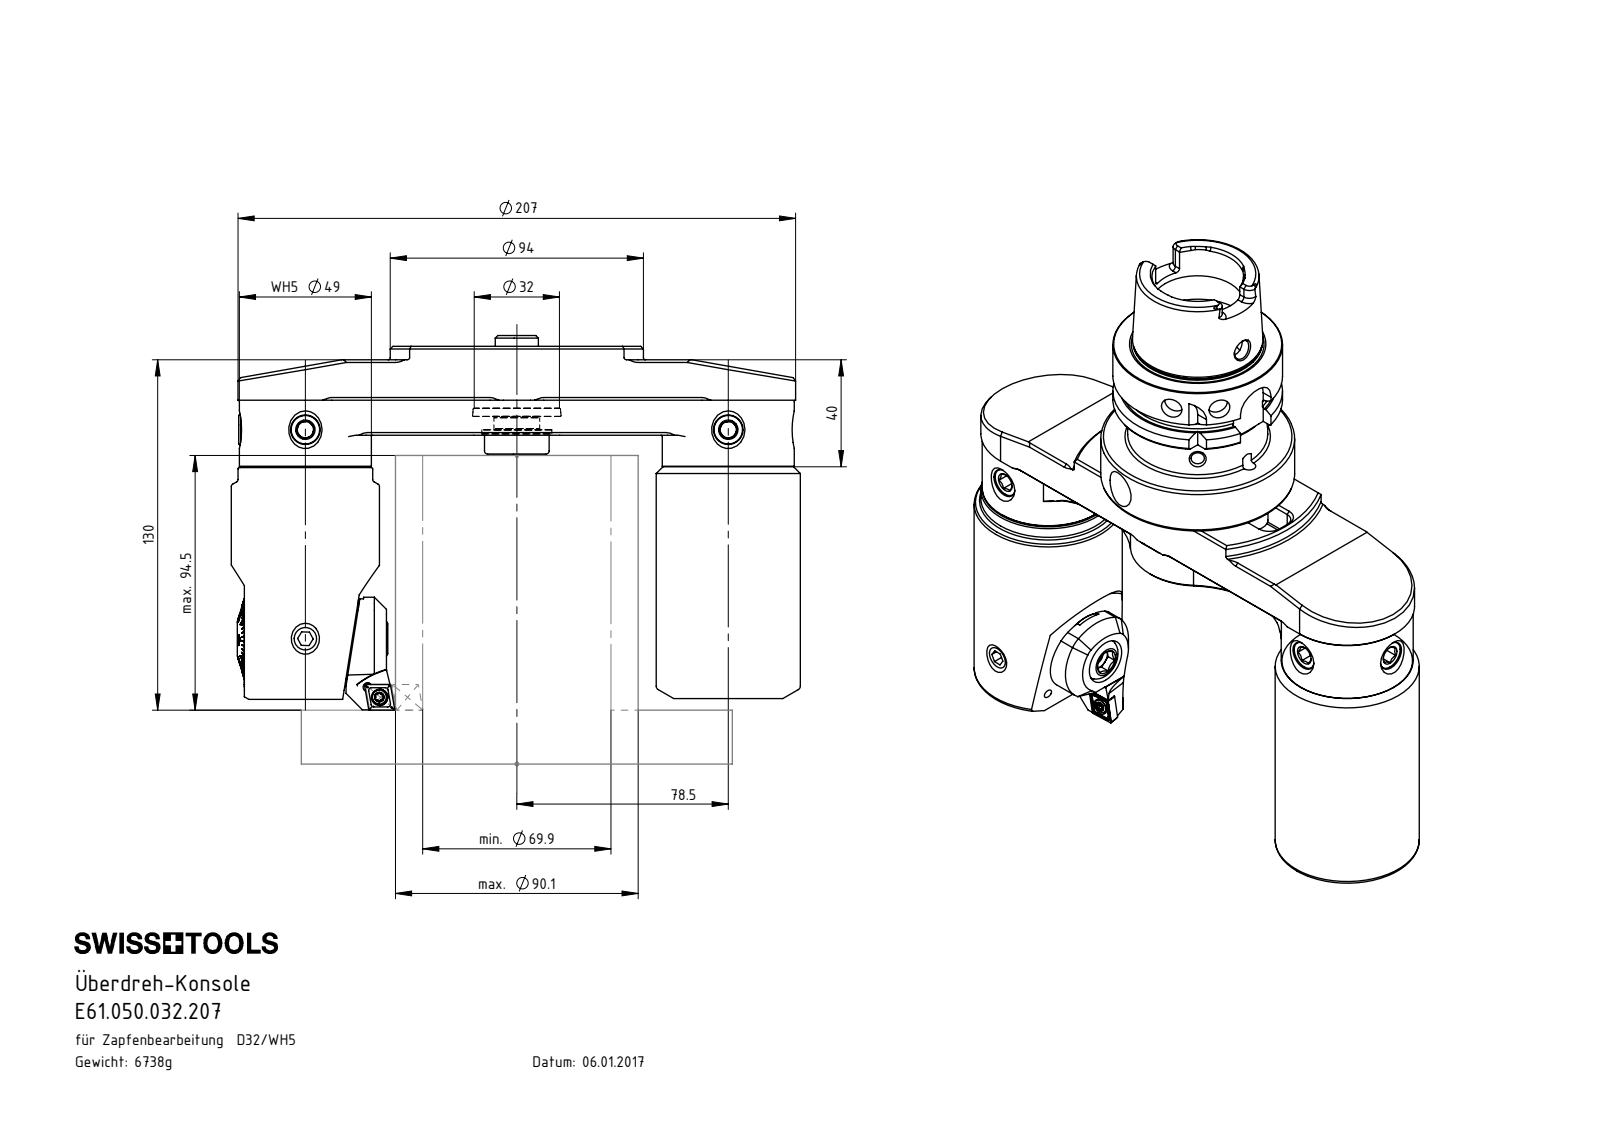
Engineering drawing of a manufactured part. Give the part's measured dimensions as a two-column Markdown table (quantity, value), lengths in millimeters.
| quantity | value |
| --- | --- |
| part name | WH5-ER1.001.017; KoU-D32.WH5.207_B_KoU-D32.WH4.145; KoU.D32.WH5.207; DIN 7984 - M16 x 35 |
| STEP written by | SolidWorks 2017 (AUTOMOTIVE_DESIGN) |
| units | millimeters |
| bodies | 6 solids, 268 faces (121 planar, 49 cylindrical, 98 other) |
| overall size | 207 × 50 × 49 |
| volume | 239 538 mm³ |
| surface area | 54 527 mm² |
| round holes (diameter × count) | 6 × 5, 11 × 3, 28 × 2, 29 × 2, 17 × 1, 26 × 1, 32 × 1, 33 × 1 |
| round bosses / shafts (diameter × count) | 12 × 3, 49 × 2, 24 × 1, 16 × 1 |
| partial cylindrical surfaces (radius × count) | 0.5 × 4, 4.5 × 4, 34.85 × 4, 25 × 3, 3.4 × 2, 47 × 1 |
| main face-to-face distances | 5, 16.5, 50, 33, 20, 12, 45, 13, 25, 40 |
| hole center spacings | 78.5, 157 |
